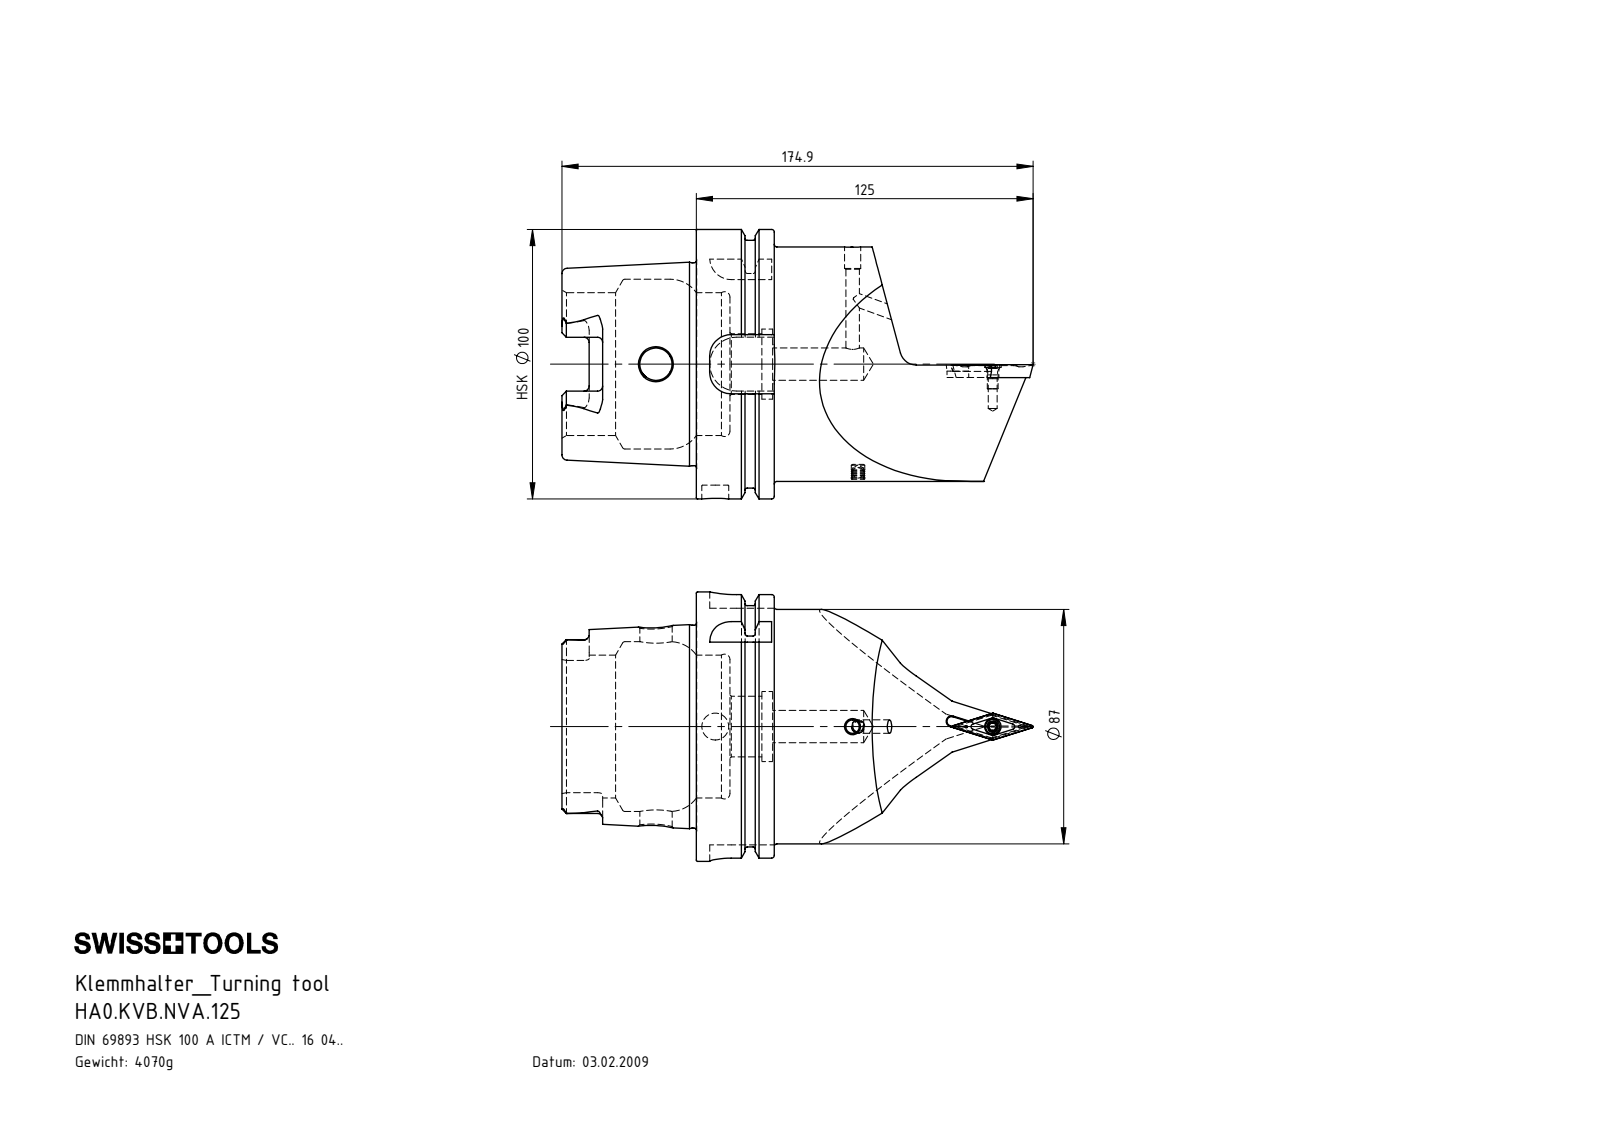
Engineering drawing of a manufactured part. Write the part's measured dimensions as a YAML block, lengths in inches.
part_name: "HA0.KVB.NVA.125; WCB-ER2.001.009_A; HA0-KVB.NVA.125_B; KVT_MB_600_050 (+1 more)"
step_written_by: "SolidWorks 2009 (CONFIG_CONTROL_DESIGN)"
units: inches
bodies: {solids: 5, faces: 302, planar: 79, cylindrical: 85, other: 138}
overall_size: [6.887, 3.937, 3.937]
volume: 31.61
surface_area: 103
round_holes:
  - {diameter: 0.197, count: 2}
  - {diameter: 0.472, count: 2}
  - {diameter: 0.13, count: 1}
  - {diameter: 0.157, count: 1}
  - {diameter: 0.173, count: 1}
  - {diameter: 0.236, count: 1}
  - {diameter: 0.24, count: 1}
  - {diameter: 0.394, count: 1}
  - {diameter: 0.886, count: 1}
  - {diameter: 1.024, count: 1}
  - {diameter: 2.087, count: 1}
  - {diameter: 2.48, count: 1}
round_bosses_or_shafts:
  - {diameter: 3.937, count: 1}
  - {diameter: 3.62, count: 1}
  - {diameter: 3.425, count: 1}
  - {diameter: 2.963, count: 1}
  - {diameter: 0.207, count: 1}
  - {diameter: 0.197, count: 1}
  - {diameter: 0.157, count: 1}
partial_cylinders:
  - {radius: 0.013, count: 6}
  - {radius: 0.023, count: 6}
  - {radius: 0.075, count: 6}
  - {radius: 0.315, count: 3}
  - {radius: 0.19, count: 2}
  - {radius: 0.192, count: 2}
  - {radius: 0.069, count: 1}
  - {radius: 0.236, count: 1}
face_to_face_distances: [0.49, 1.14, 0.65, 1.965, 2.455, 3.104, 3.457, 3.079, 1.114, 0.624]
hole_center_spacings: [0.079, 1.968, 1.972, 2.008, 2.047, 2.051, 2.087, 4.055]
